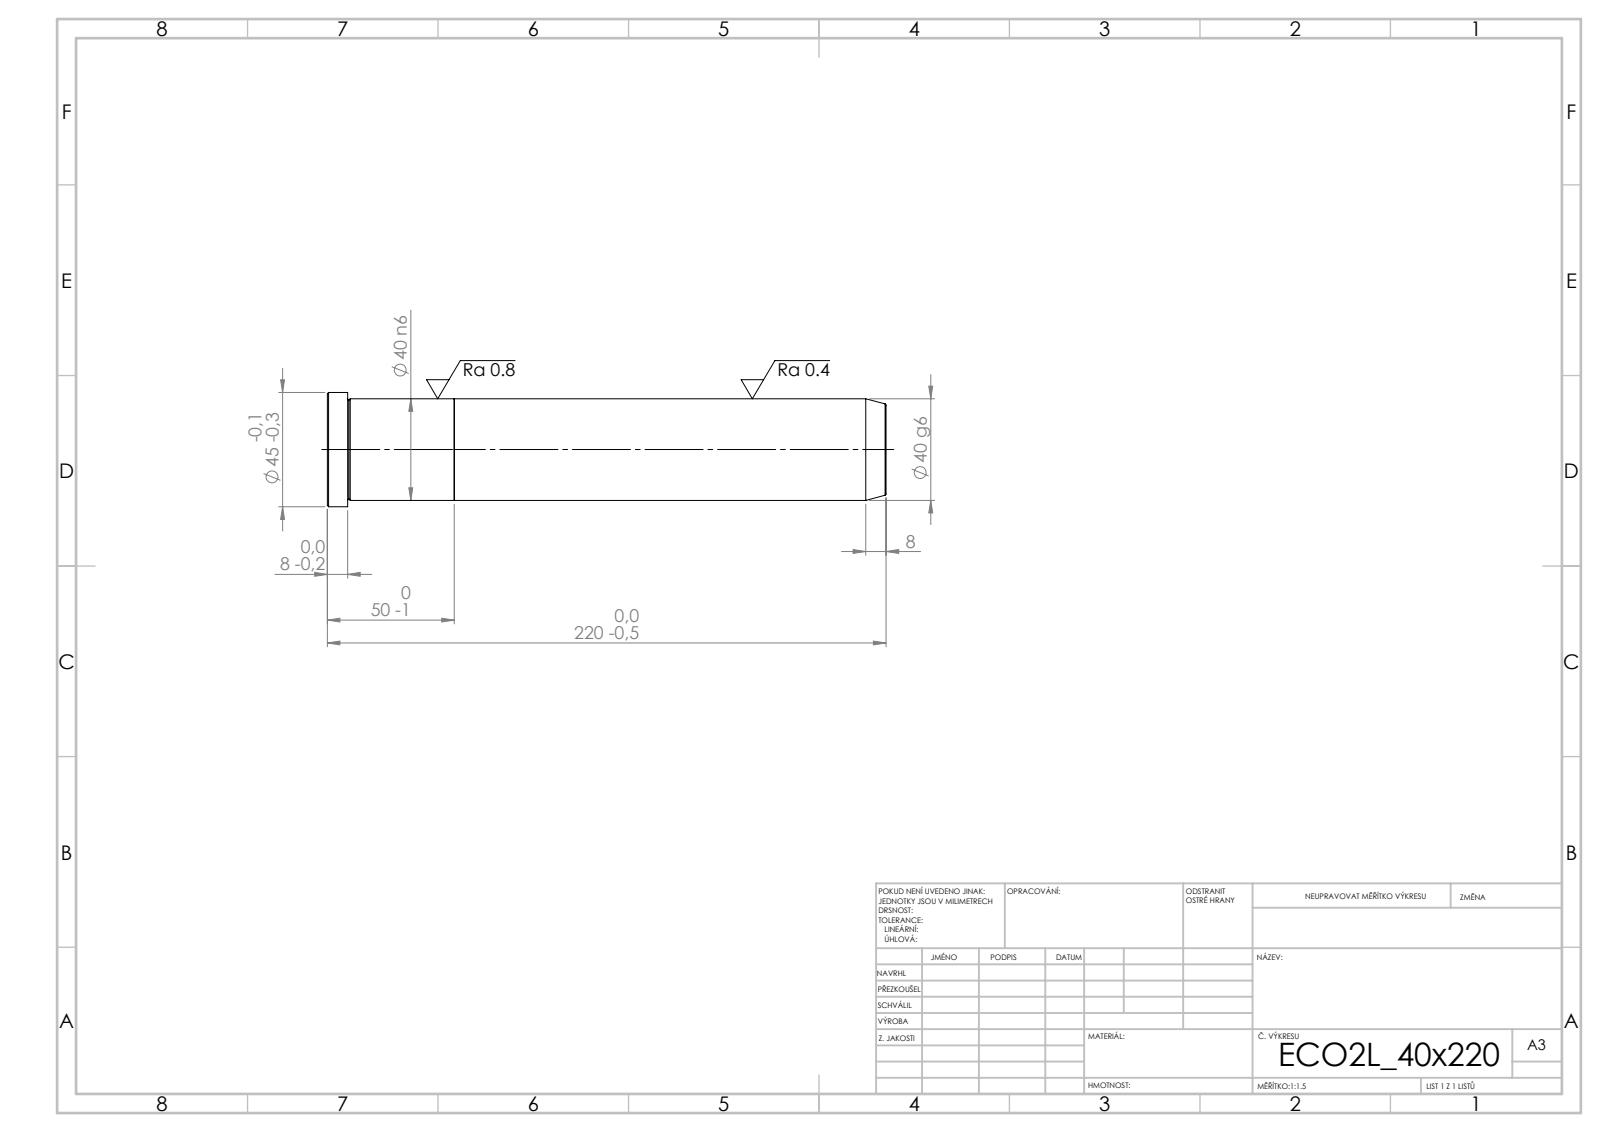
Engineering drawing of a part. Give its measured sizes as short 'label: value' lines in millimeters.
written by: SolidWorks 2019 (CONFIG_CONTROL_DESIGN)
unit: mm
bodies: 2 solids, 21 faces (5 planar, 6 cylindrical, 10 other)
size: 220 × 45 × 45
volume: 278 022 mm³; area: 33 205 mm²
bosses: 1× ⌀45, 1× ⌀40
face distances: 50, 170, 220, 212, 42, 8
